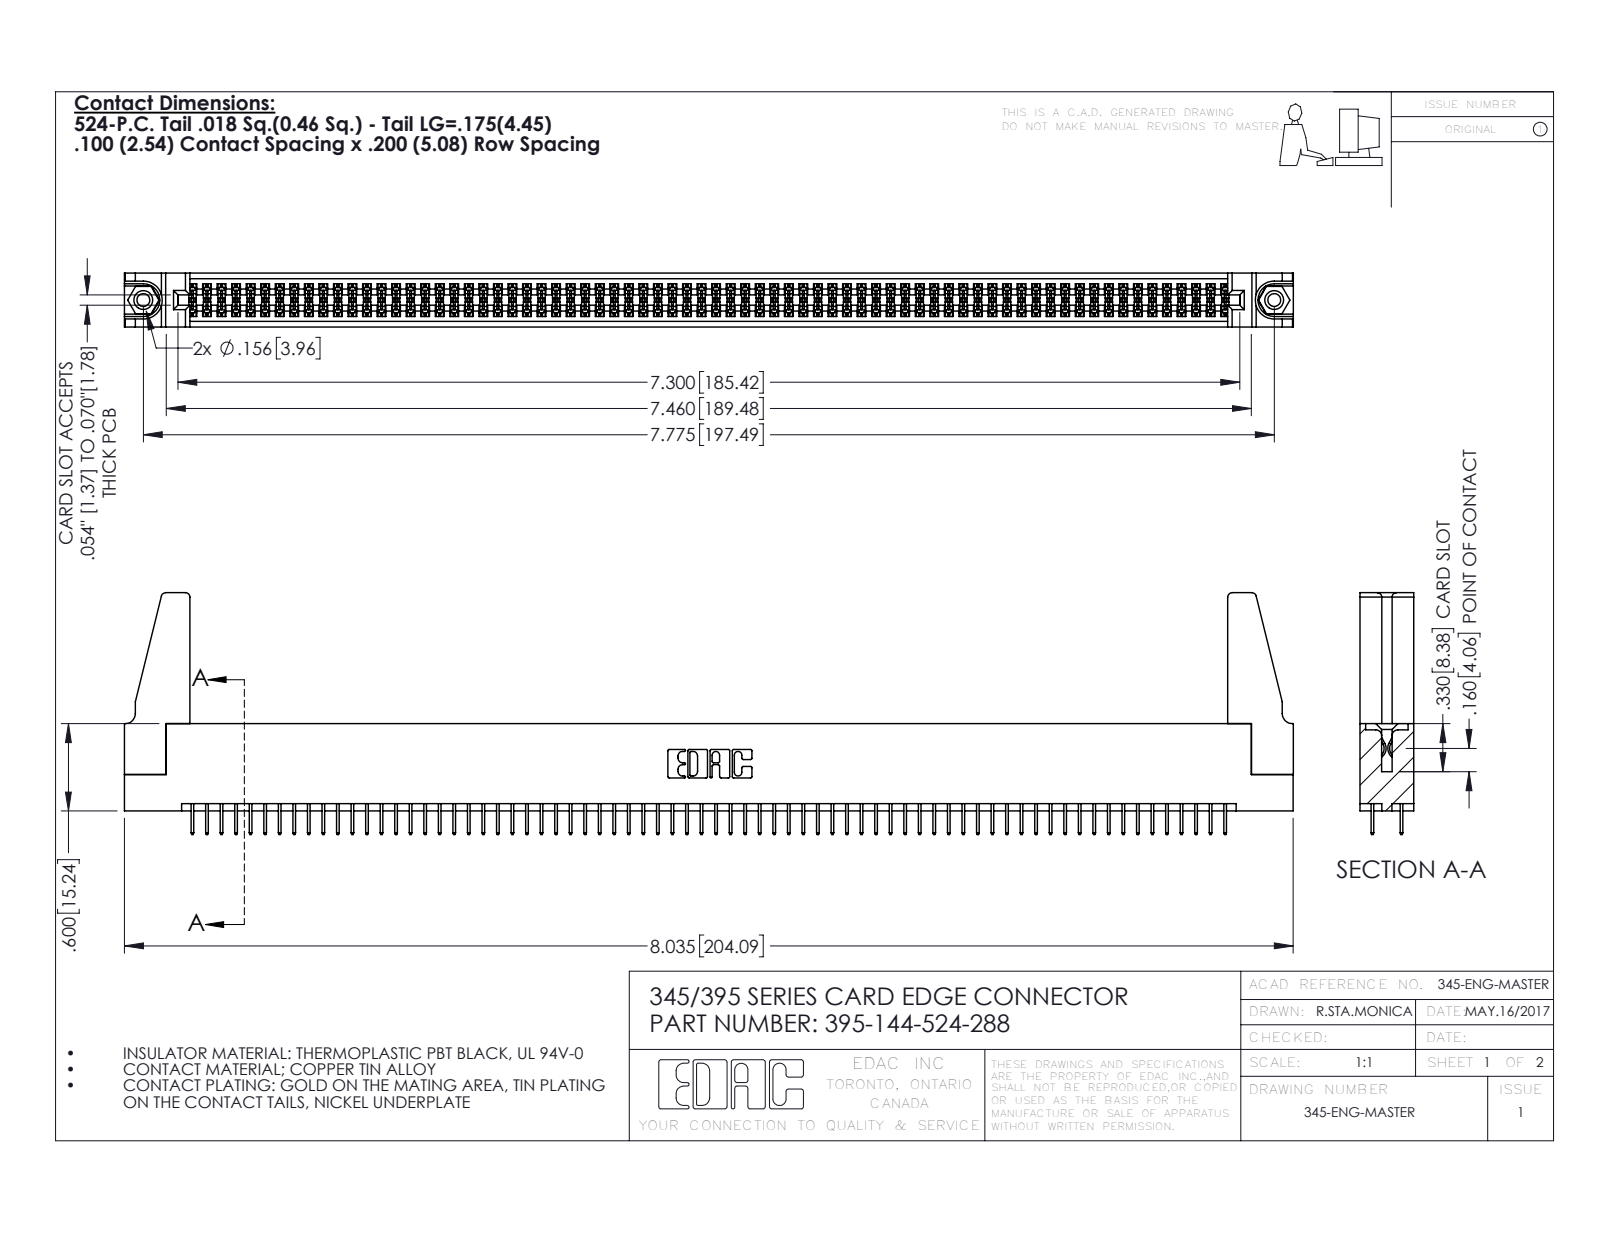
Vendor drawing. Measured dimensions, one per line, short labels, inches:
name: 345-220-078_345-220-088; 345-292-001_345-293-124; 345 Part_Flush Mounting Lugs - 0.156 Dia-TH; 395-144-524-288 (+1 more)
written by: SolidWorks 2016 (CONFIG_CONTROL_DESIGN)
unit: in
bodies: 149 solids, 8026 faces (5768 planar, 2242 cylindrical, 16 other)
size: 8.036 × 1.662 × 0.37
volume: 1.412 in³; area: 50.42 in²
holes: 2× ⌀0.089, 2× ⌀0.125, 2× ⌀0.156, 1× ⌀0.064
bosses: 2× ⌀0.155
rounds: 216× R0.006, 22× R0.01, 8× R0.03, 6× R0.007, 6× R0.031, 3× R0.026, 2× R0.014, 2× R0.019
face distances: 0.072, 0.298, 0.37, 0.2, 0.098, 0.272, 0.025, 0.225, 0.072, 0.175
hole spacings: 0.27, 7.539, 7.775
